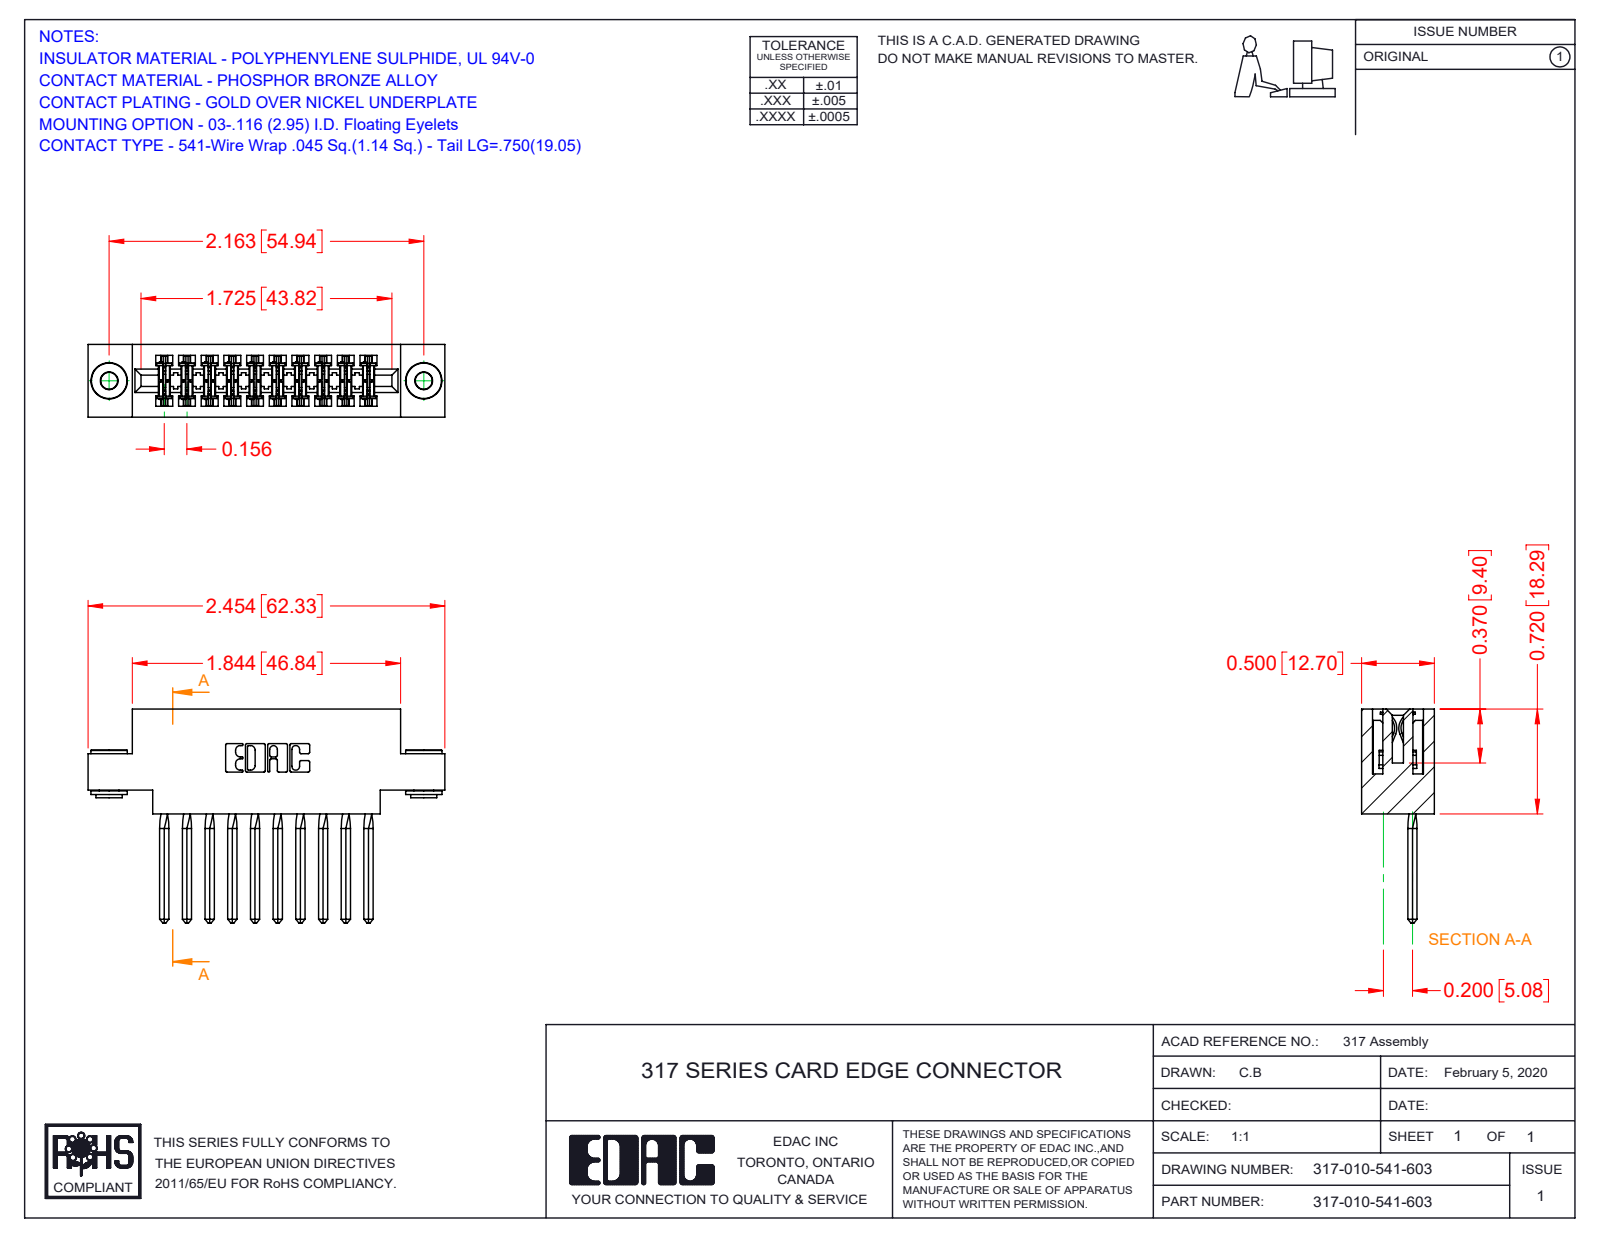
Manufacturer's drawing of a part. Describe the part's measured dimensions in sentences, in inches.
The part is named "317-290-002_541; 345-250-002_345-250-002-102; 317 Part_.156 Dia - TH; 317-010-541-603". Its 3-D file was written by "SolidWorks 2016 (CONFIG_CONTROL_DESIGN)". It is 13 solids with 1660 faces: 1308 planar, 304 cylindrical and 48 other. Overall it measures 2.454 by 1.47 by 0.5 inches. Its volume is 0.558 cubic inches and its surface area 18.71 square inches. Round holes: 2 of diameter 0.116, 2 of diameter 0.156. Round bosses or shafts: 2 of diameter 0.25, 2 of diameter 0.18, 2 of diameter 0.136. Partial cylindrical surfaces (rounded edges, fillets, slot ends): 22 of radius 0.01, 20 of radius 0.015, 6 of radius 0.007, 6 of radius 0.031, 3 of radius 0.026, 2 of radius 0.095, 2 of radius 0.1, 2 of radius 0.11. The main face-to-face distances are 0.5, 0.075, 0.425, 0.11, 0.065, 0.22, 0.331, 0.35, 0.156, 0.305. The hole center spacings are 2.163.
